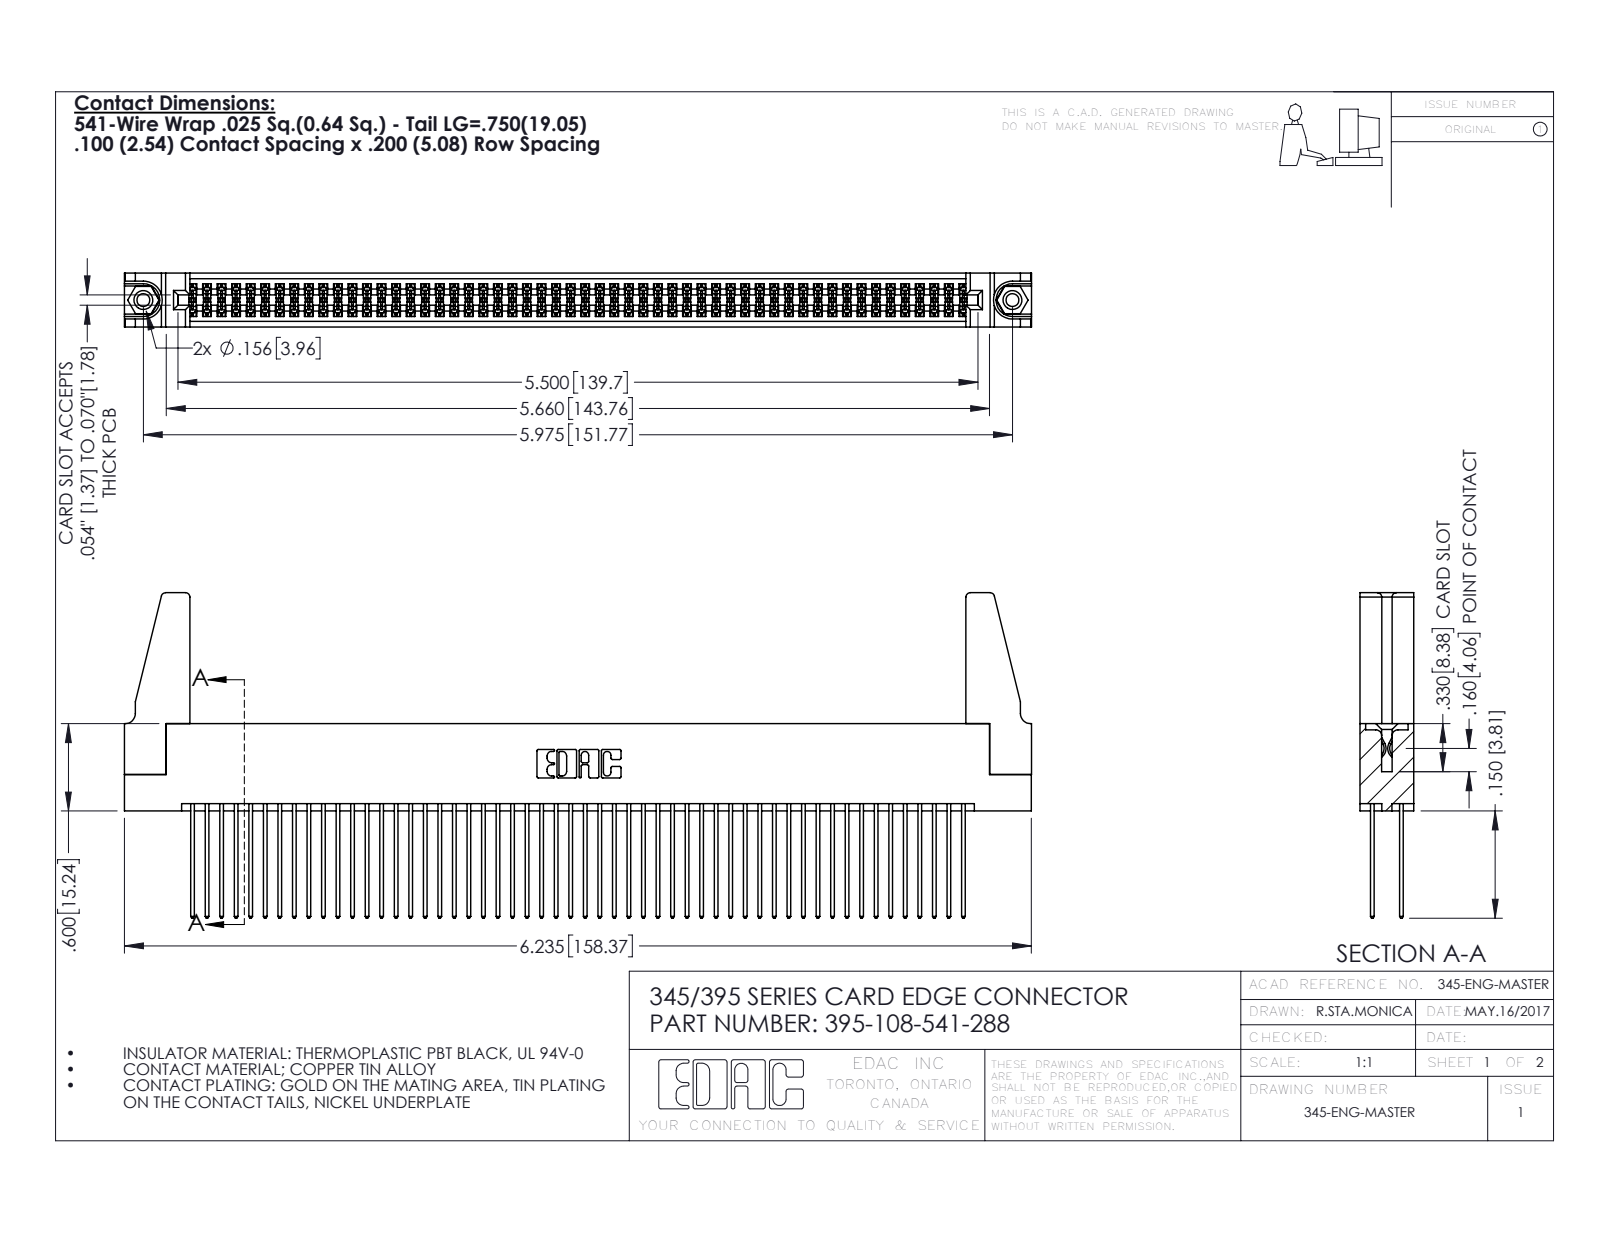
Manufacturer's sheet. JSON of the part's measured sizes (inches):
{"part_name": "345-220-078_345-220-088; 345-292-001_345-293-141; 395-108-541-288; 345 Part_Flush Mounting Lugs - 0.156 Dia-TH (+1 more)", "step_written_by": "SolidWorks 2016 (CONFIG_CONTROL_DESIGN)", "units": "inches", "bodies": {"solids": 113, "faces": 5650, "planar": 3716, "cylindrical": 1918, "other": 16}, "overall_size": [6.236, 2.237, 0.37], "volume_in3": 1.182, "surface_area_in2": 46.64, "round_holes": [[0.089, 2], [0.125, 2], [0.156, 2], [0.064, 1]], "round_bosses_or_shafts": [[0.155, 2]], "partial_cylinders_radius": [[0.006, 162], [0.01, 108], [0.01, 22], [0.03, 8], [0.007, 6], [0.031, 6], [0.026, 3], [0.014, 2]], "face_to_face_distances": [0.072, 0.298, 0.2, 0.098, 0.272, 0.025, 0.37, 0.225, 0.175, 0.149], "hole_center_spacings": [0.27, 5.739, 5.975]}
